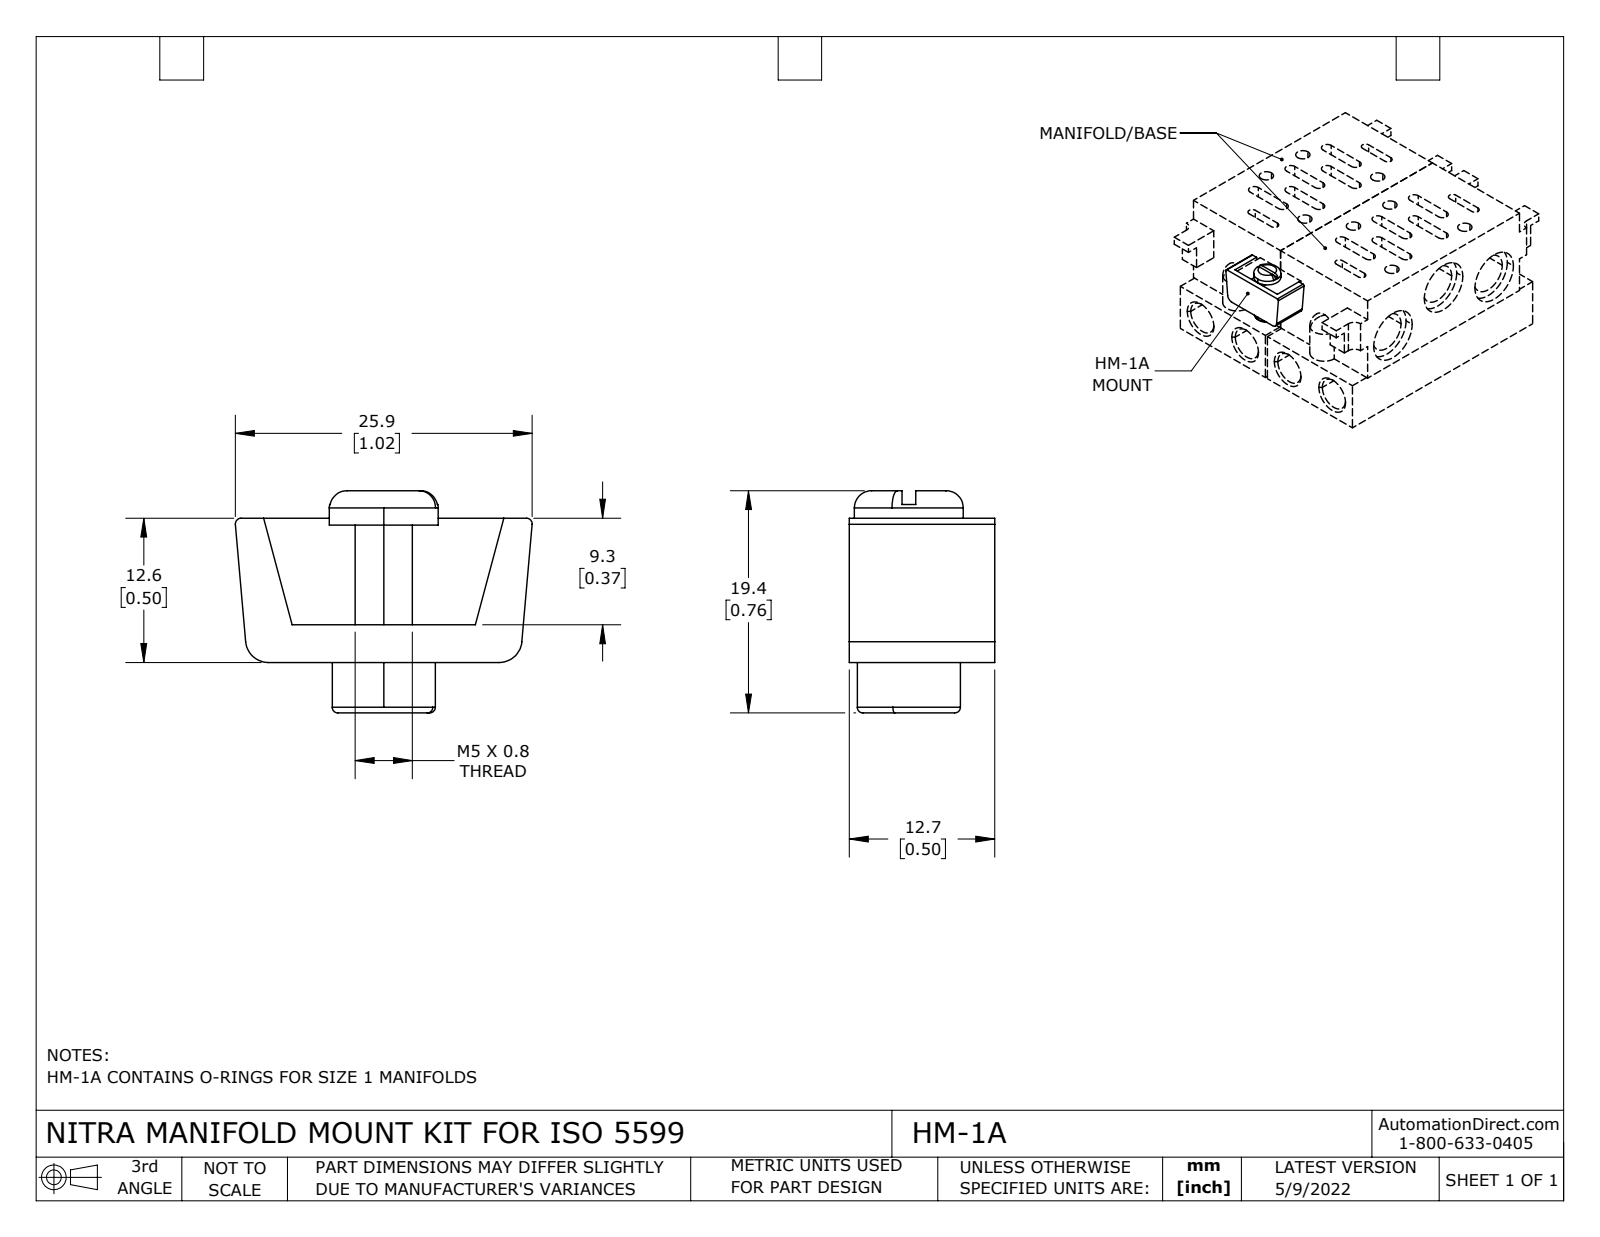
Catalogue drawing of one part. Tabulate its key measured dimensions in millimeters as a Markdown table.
| quantity | value |
| --- | --- |
| part name | HM-1A |
| STEP written by | SolidWorks 2021 (CONFIG_CONTROL_DESIGN) |
| units | millimeters |
| bodies | 1 solid, 38 faces (18 planar, 12 cylindrical, 8 other) |
| overall size | 25.91 × 19.4 × 12.7 |
| volume | 2 755 mm³ |
| surface area | 2 156 mm² |
| round holes (diameter × count) | 4.13 × 1 |
| round bosses / shafts (diameter × count) | 9.5 × 1, 9 × 1, 5 × 1 |
| partial cylindrical surfaces (radius × count) | 0.5 × 2, 2 × 2 |
| main face-to-face distances | 2, 3.3, 12.7, 10.7, 12.6, 9.3, 12, 8.7, 0.6, 1.2 |
